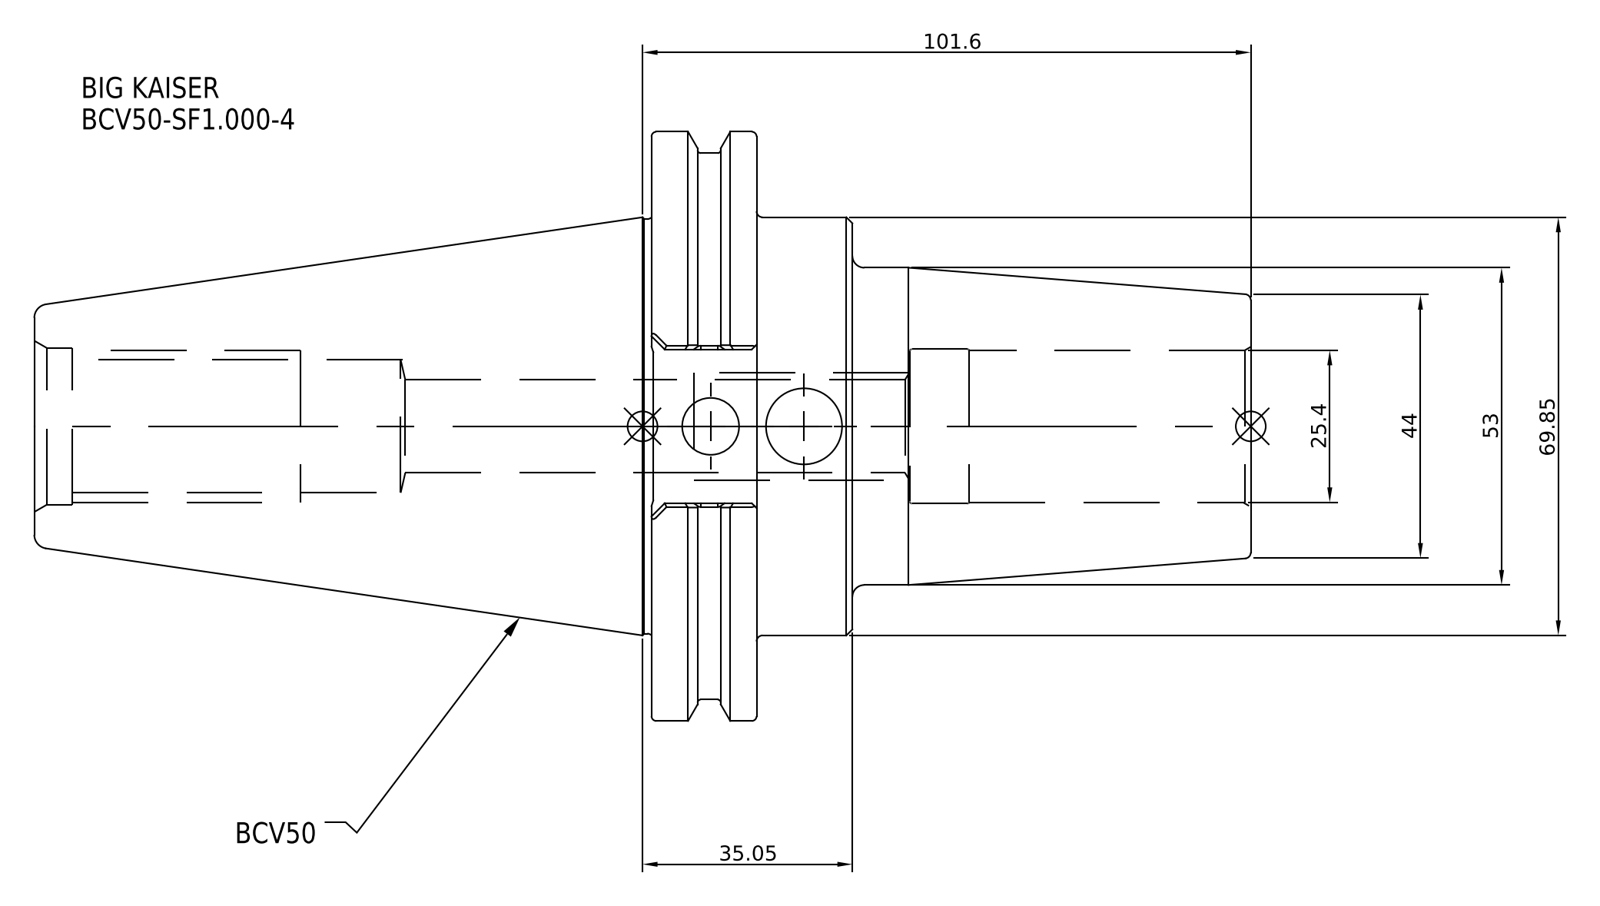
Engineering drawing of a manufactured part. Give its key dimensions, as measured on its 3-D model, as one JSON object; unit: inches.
{"part_name": "BCV50-SF1_000-4", "step_written_by": "SolidWorks 2021 (CONFIG_CONTROL_DESIGN)", "units": "inches", "bodies": {"solids": 1, "faces": 30, "planar": 8, "cylindrical": 14, "other": 8}, "overall_size": [8, 3.875, 3.875], "volume_in3": 33.29, "surface_area_in2": 84.24, "round_holes": [[1, 1]], "round_bosses_or_shafts": [[3.875, 1], [3.594, 1], [2.75, 1], [2.087, 1]], "face_to_face_distances": [0.691, 0.63, 1.321, 5.38, 4.75, 4.059, 2.62, 3.25, 3.941, 8]}
